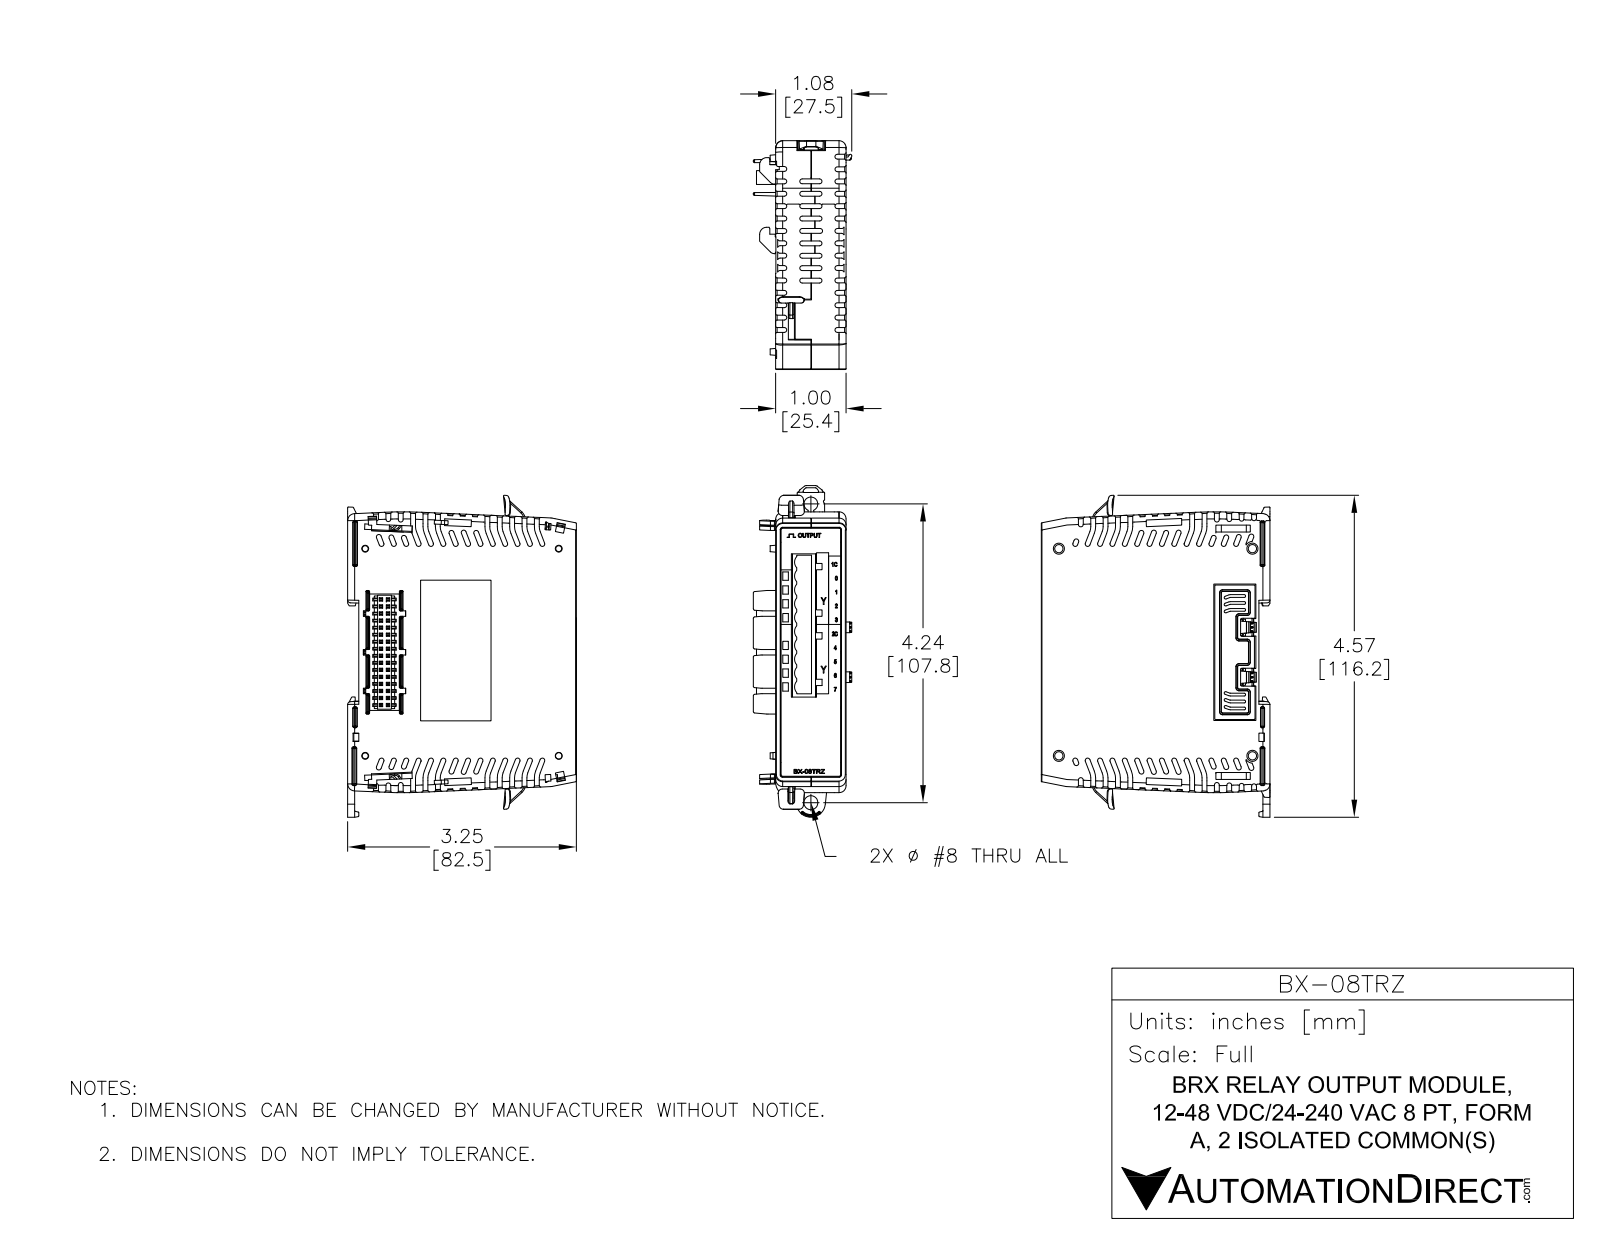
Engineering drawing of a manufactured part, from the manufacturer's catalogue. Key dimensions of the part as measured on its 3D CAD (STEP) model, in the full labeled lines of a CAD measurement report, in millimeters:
Part name (STEP PRODUCT): BX-08TRZ door mod 1 comb1 fXT c
STEP written by: SolidWorks 2017 (AUTOMOTIVE_DESIGN)
Units: millimetres
Bodies: 26 solids, 3322 faces (2530 planar, 377 cylindrical, 415 other)
Overall size (bounding box): 116.5 × 84.1 × 35.6
Volume: 189 900 mm³ · Surface area: 47 050 mm²
Round holes (diameter × count): ⌀1.2 ×2, ⌀1.7 ×2, ⌀3 ×2, ⌀3 ×2, ⌀5.1 ×1
Round bosses / shafts (diameter × count): ⌀1.6 ×2, ⌀1.5 ×2
Partial cylindrical surfaces — rounded edges, fillets, slot ends (radius × count): R0.3 ×46, R0.1 ×24, R0.5 ×22, R0.2 ×21, R3 ×14, R1 ×13, R0.3 ×12, R0.4 ×12
Main face-to-face distances: 25.4, 81.6, 81.8, 1, 12.1, 2.5, 4, 77.5, 77.8, 1.3
Hole centre spacings: 2.5, 20.9, 23.3, 33, 53.2, 55.7, 65.7, 66.5
